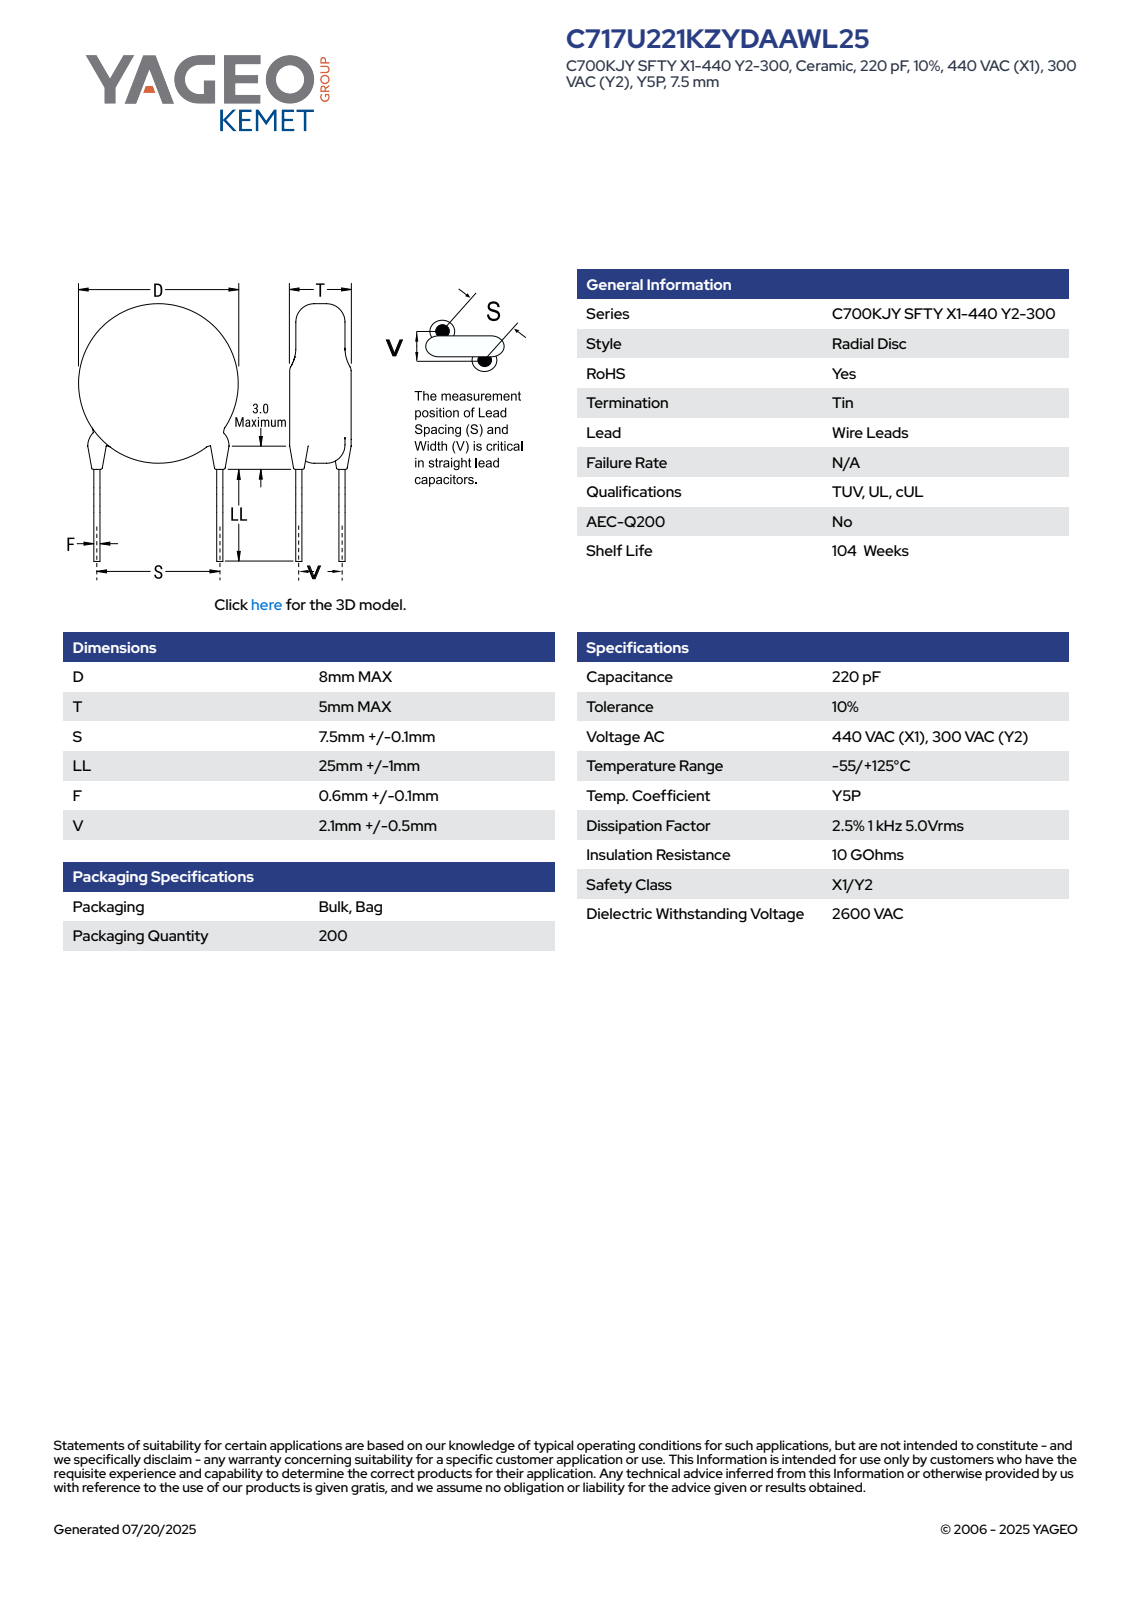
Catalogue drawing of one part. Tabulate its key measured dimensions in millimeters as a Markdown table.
| quantity | value |
| --- | --- |
| part name | CCD_KST_8X5_D8T5S7.6LL26F0.7V2.1 |
| STEP written by | SolidWorks 2021 (AUTOMOTIVE_DESIGN) |
| units | millimeters |
| bodies | 4 solids, 81 faces (63 planar, 14 cylindrical, 4 other) |
| overall size | 35.5 × 8.7 × 5 |
| volume | 269 mm³ |
| surface area | 351 mm² |
| round bosses / shafts (diameter × count) | 1.2 × 4, 0.7 × 2, 8 × 1 |
| main face-to-face distances | 5, 26, 0.97, 32.02, 6.02, 31.05, 5.05, 0.36, 0.78, 3.96 |
